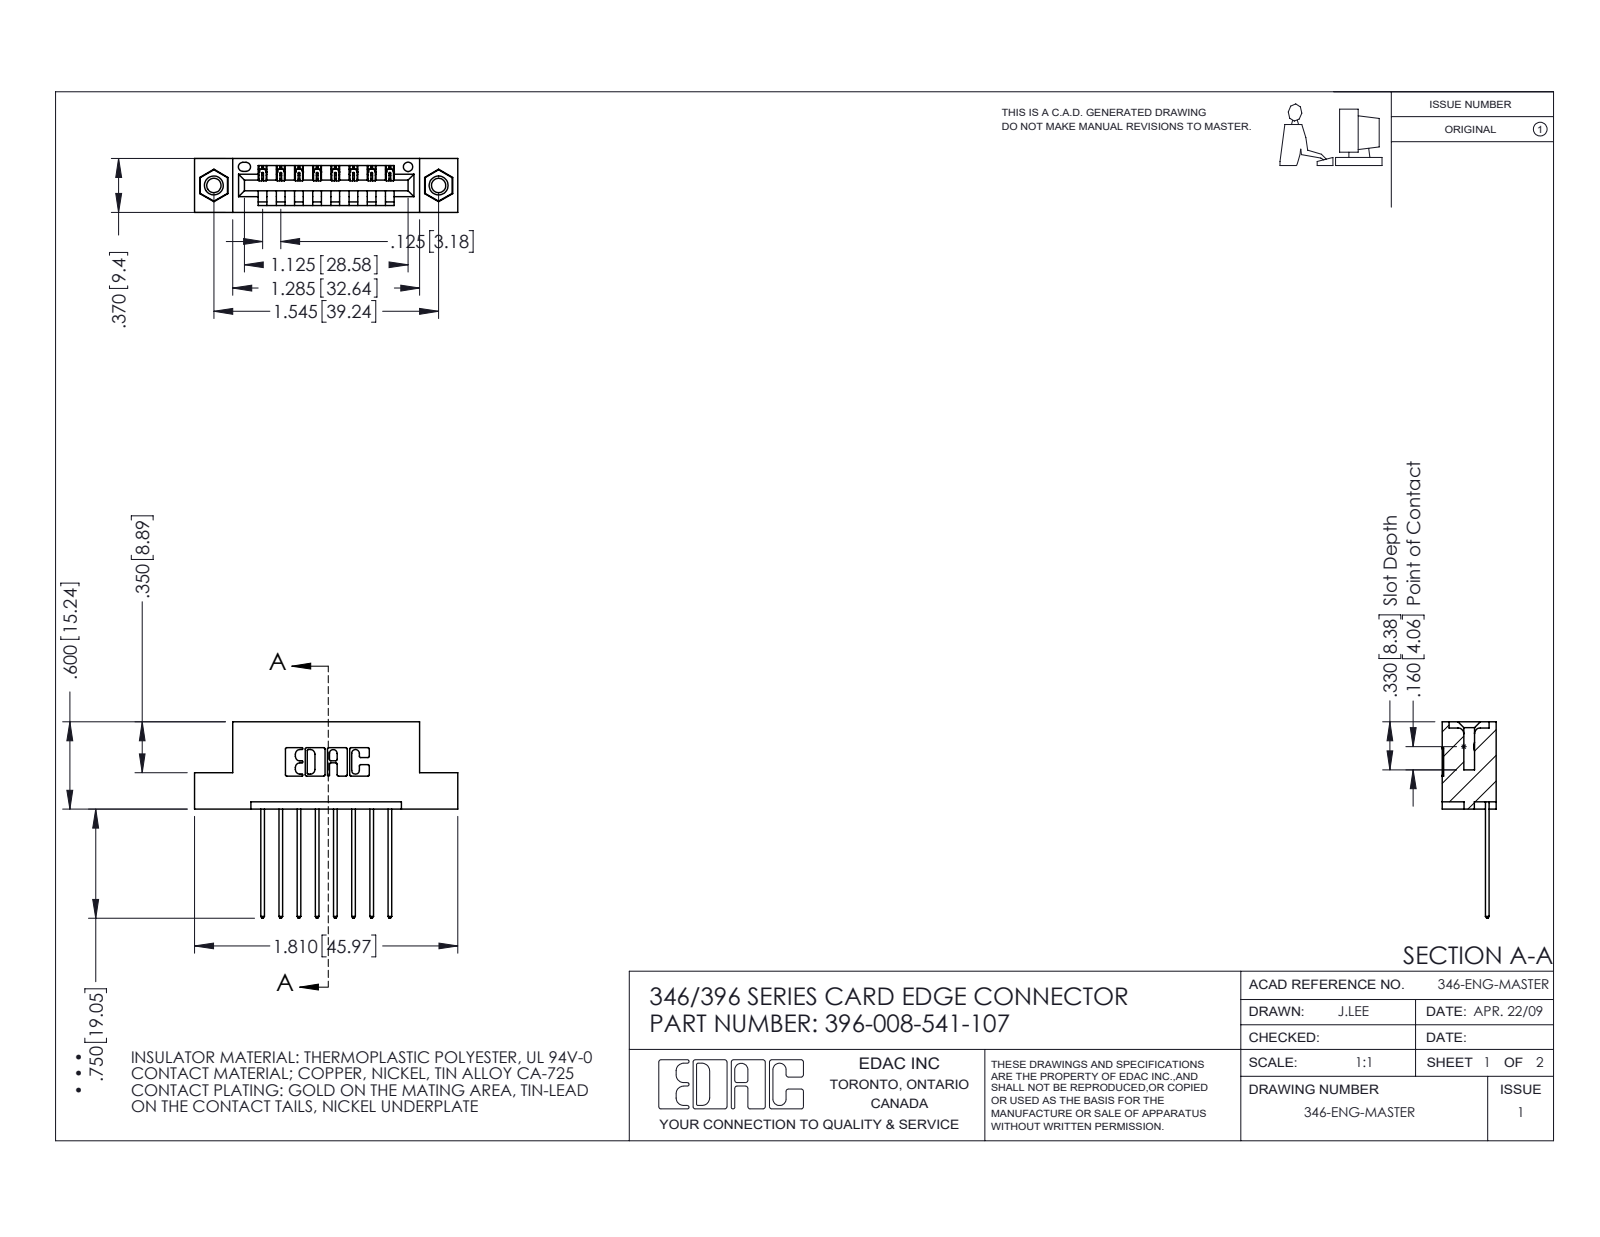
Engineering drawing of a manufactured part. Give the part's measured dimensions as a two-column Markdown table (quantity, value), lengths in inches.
| quantity | value |
| --- | --- |
| part name | 396-008-541-107; 346 Part_Flush Mounting Lugs - 0.156 Dia-TI; 345-250-001_345-250-005-103; 345-292-001_345-293-141 |
| STEP written by | SolidWorks 2016 (CONFIG_CONTROL_DESIGN) |
| units | inches |
| bodies | 11 solids, 646 faces (428 planar, 202 cylindrical, 16 other) |
| overall size | 1.81 × 1.35 × 0.37 |
| volume | 0.255 in³ |
| surface area | 7.826 in² |
| round holes (diameter × count) | 0.098 × 2, 0.125 × 2, 0.156 × 2, 0.064 × 1 |
| round bosses / shafts (diameter × count) | 0.155 × 2 |
| partial cylindrical surfaces (radius × count) | 0.01 × 22, 0.006 × 16, 0.01 × 16, 0.007 × 6, 0.031 × 6, 0.026 × 3, 0.031 × 2, 0.04 × 2 |
| main face-to-face distances | 0.25, 0.048, 0.322, 0.37, 0.072, 0.298, 0.025, 0.5, 0.148, 0.222 |
| hole center spacings | 0.246, 1.341, 1.545 |
